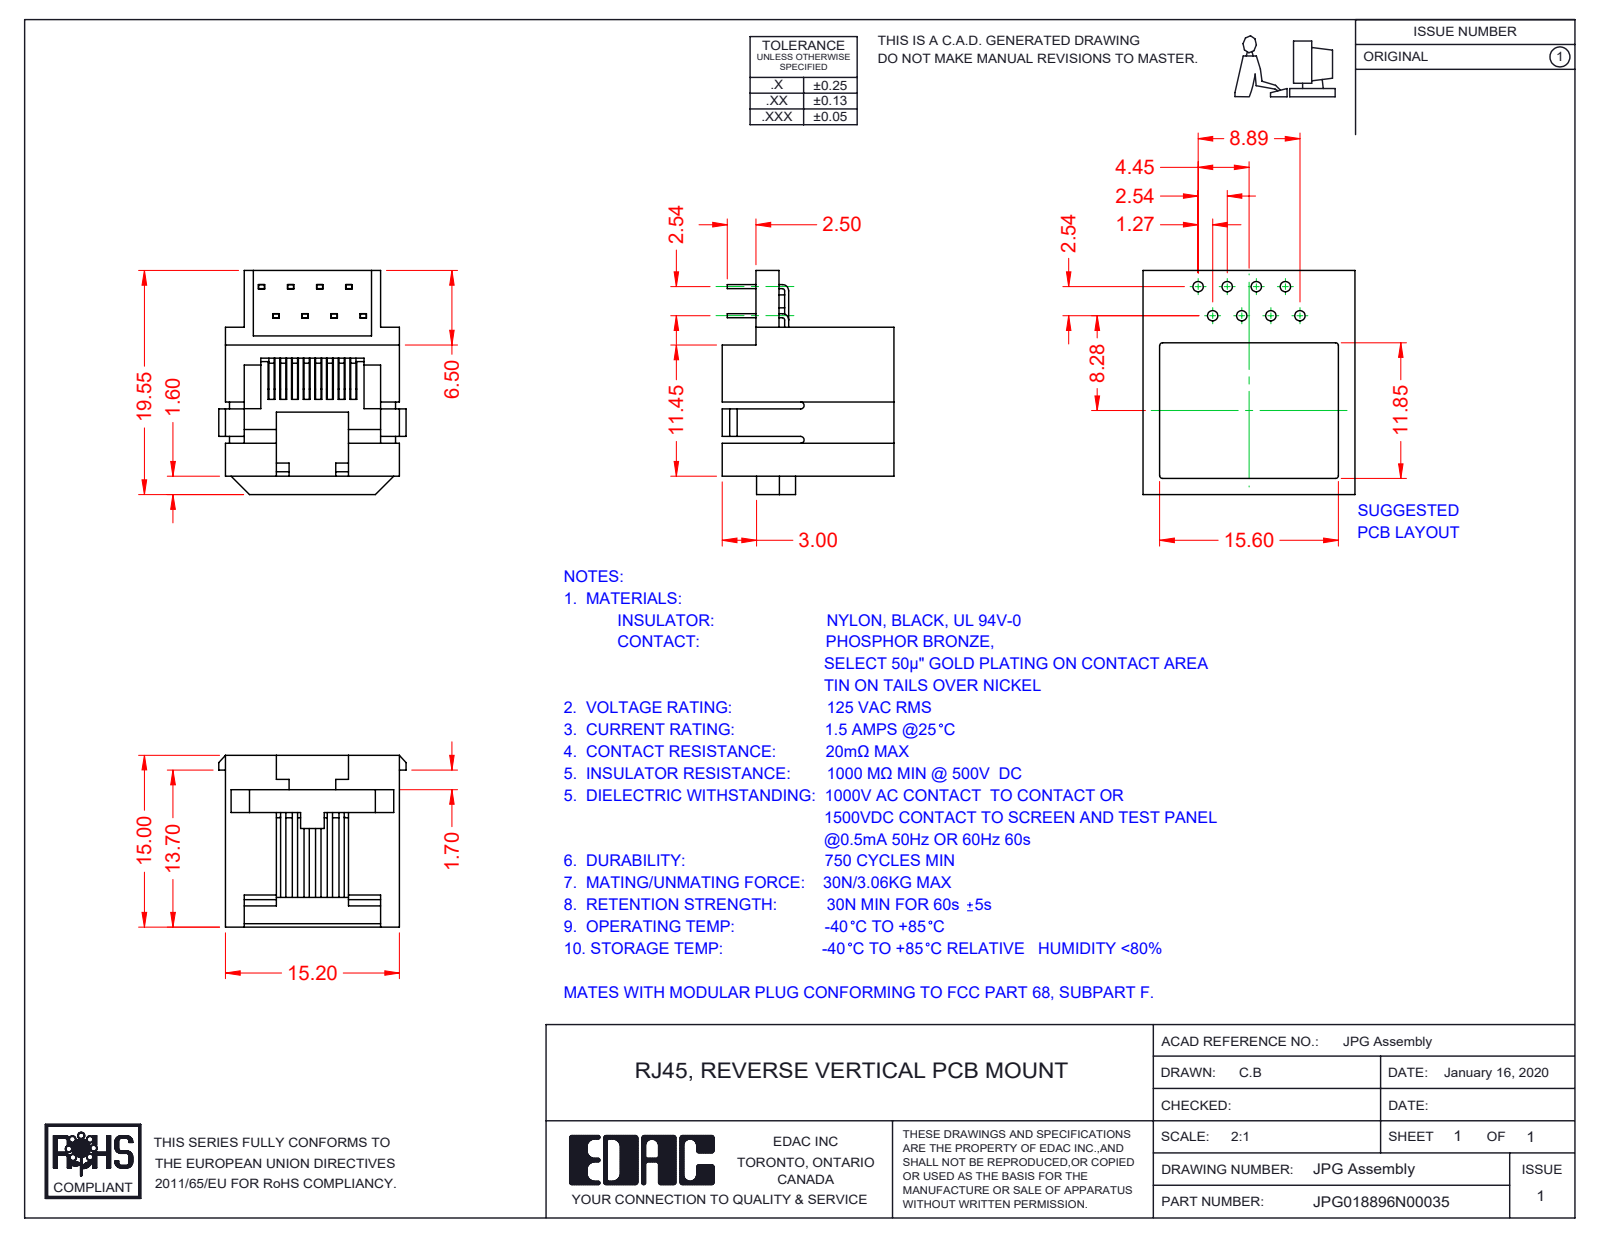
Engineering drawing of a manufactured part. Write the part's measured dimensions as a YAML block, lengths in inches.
part_name: "PG Contact Lock; PG Contacts; PG Insulator; JPG018896N00035"
step_written_by: "SolidWorks 2016 (CONFIG_CONTROL_DESIGN)"
units: inches
bodies: {solids: 10, faces: 542, planar: 461, cylindrical: 69, other: 12}
overall_size: [0.77, 0.644, 0.591]
volume: 0.085
surface_area: 4.196
partial_cylinders:
  - {radius: 0.012, count: 3}
  - {radius: 0.008, count: 2}
  - {radius: 0.014, count: 2}
  - {radius: 0.022, count: 2}
  - {radius: 0.028, count: 2}
face_to_face_distances: [0.014, 0.065, 0.534, 0.406, 0.598, 0.102, 0.071, 0.024, 0.053, 0.508]
